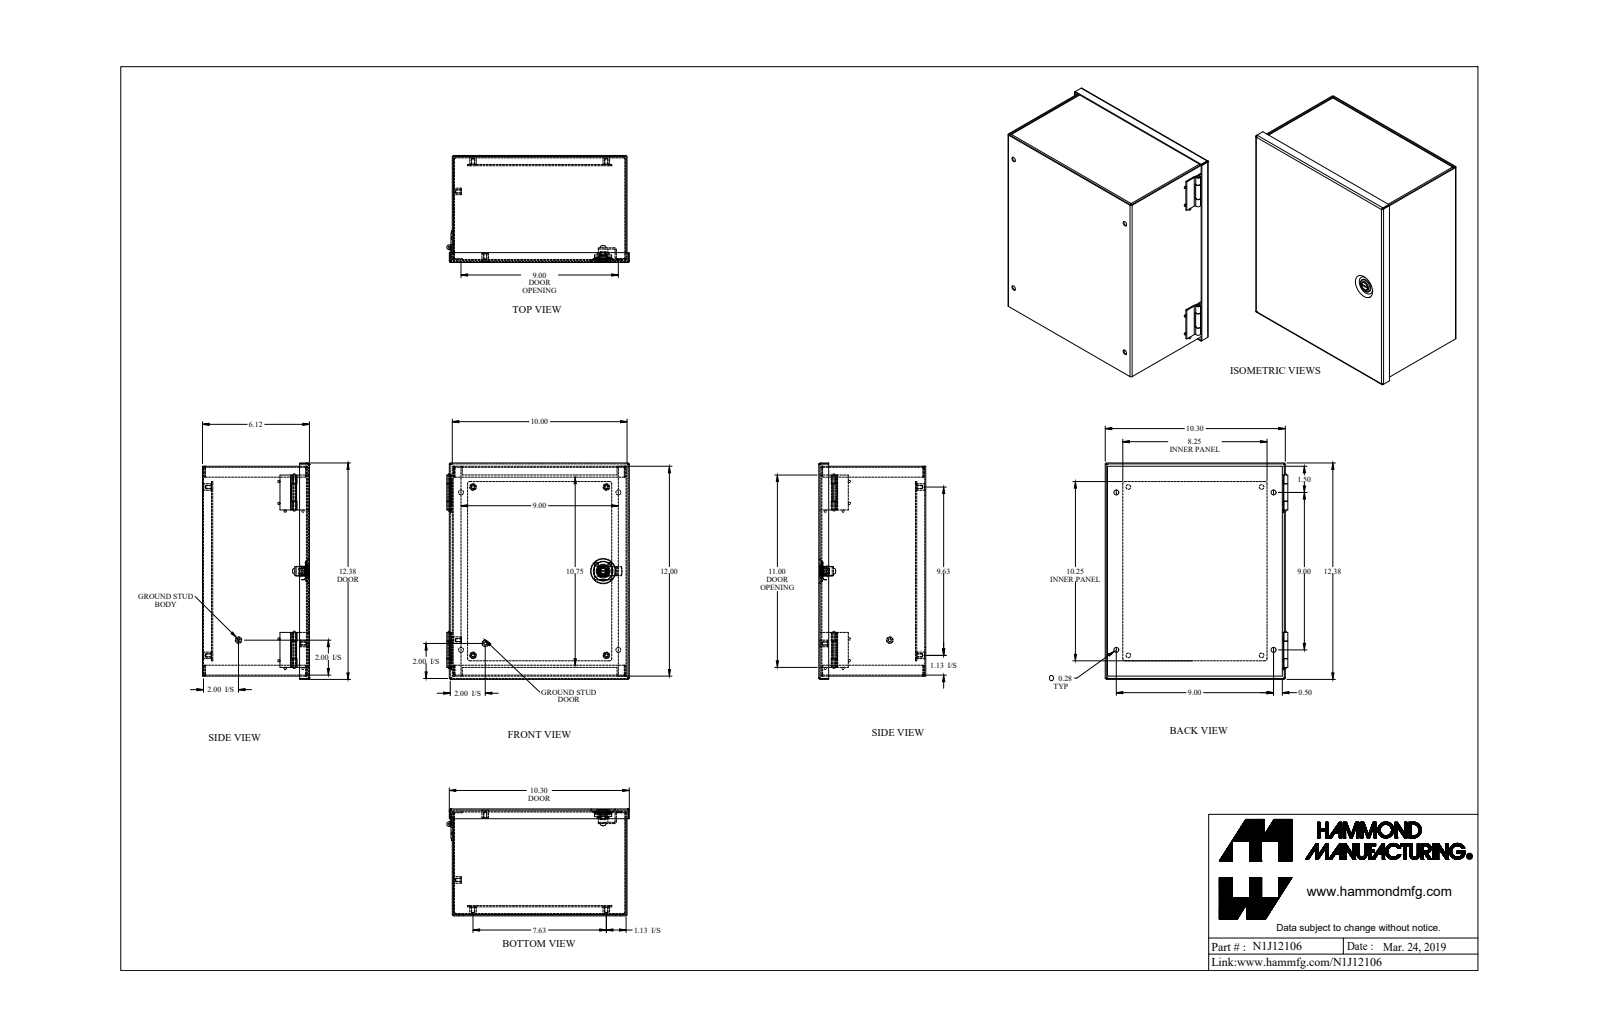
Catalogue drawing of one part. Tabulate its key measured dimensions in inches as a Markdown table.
| quantity | value |
| --- | --- |
| part name | N1J12106 |
| STEP written by | SolidWorks 2018 (AUTOMOTIVE_DESIGN) |
| units | inches |
| bodies | 18 solids, 477 faces (224 planar, 188 cylindrical, 65 other) |
| overall size | 12.38 × 10.443 × 6.118 |
| volume | 39.65 in³ |
| surface area | 1 351 in² |
| round holes (diameter × count) | 0.156 × 6, 0.265 × 4, 0.28 × 4, 0.125 × 1, 0.319 × 1, 0.476 × 1 |
| round bosses / shafts (diameter × count) | 0.131 × 8, 0.375 × 6, 0.787 × 1, 0.547 × 1, 0.472 × 1, 0.469 × 1, 0.366 × 1, 0.32 × 1 |
| partial cylindrical surfaces (radius × count) | 0.029 × 16, 0.086 × 16, 0.012 × 4, 0.1 × 4, 0.125 × 4, 0.036 × 2, 0.079 × 2, 0.25 × 2 |
| main face-to-face distances | 0.057, 6.061, 9.943, 6.004, 6.118, 11.943, 0.072, 0.517, 0.46, 5.544 |
| hole center spacings | 0.755, 8.319, 9, 9.338, 12.483, 4.583, 4.816, 7.625 |
